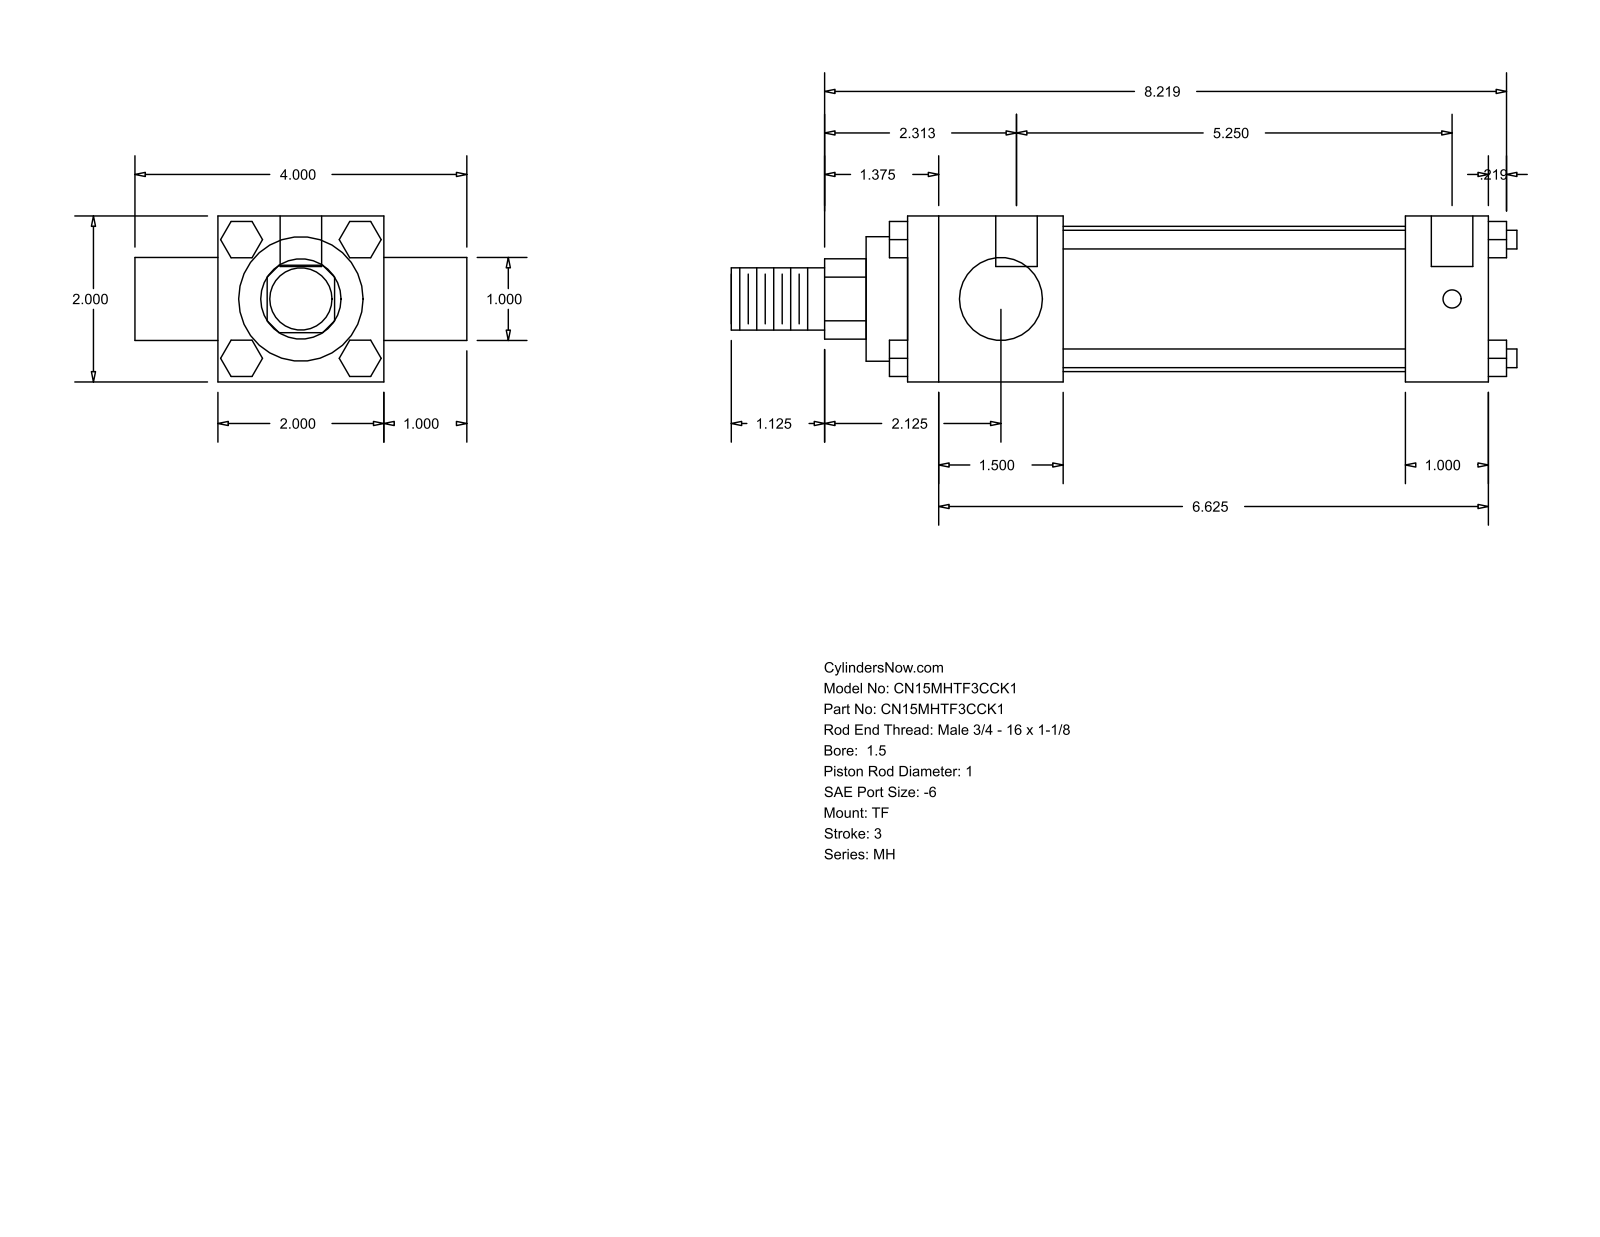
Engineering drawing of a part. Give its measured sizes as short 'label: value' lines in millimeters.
name: MH_TF__0150_1
written by: GSSL Pune (CONFIG_CONTROL_DESIGN)
unit: mm
bodies: 0 solids, 120 faces (92 planar, 28 cylindrical, 0 other)
size: 240.51 × 101.6 × 50.8
holes: 3× ⌀5.56, 2× ⌀12.7
bosses: 4× ⌀5.71, 2× ⌀25.4, 1× ⌀44.45, 1× ⌀38.1, 1× ⌀19.05
rounds: 1× R12.29
face distances: 50.8, 25.4, 177.8, 76.2, 47.63, 130.17, 152.4, 104.77, 101.6, 12.7
hole spacings: 3.18, 133.35, 136.53
